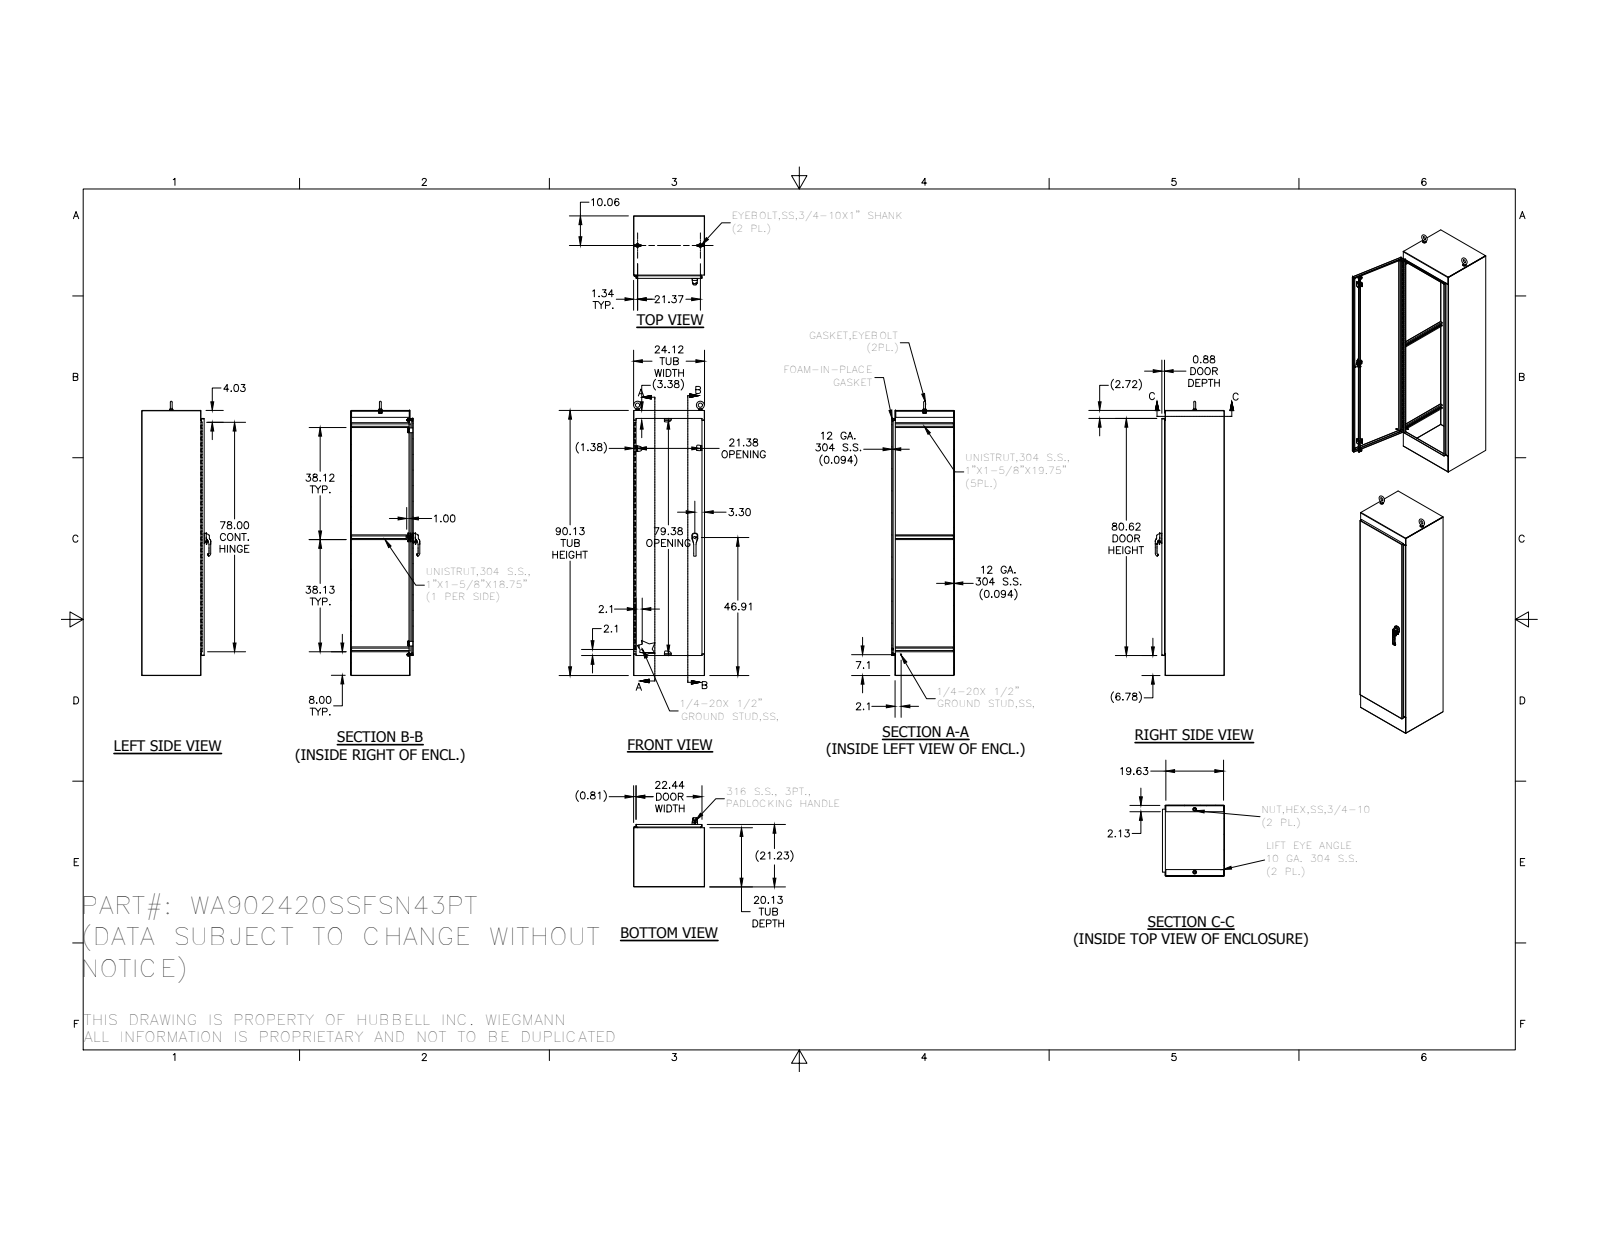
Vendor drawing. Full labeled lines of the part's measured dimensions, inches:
Part name (STEP PRODUCT): PLASTIC-ROLLER-CAM_AF0_ASM; 1091-903_AF0_2; DIN3771_16X2_5; 1091-76 (+8 more)
STEP written by: SolidWorks 2014 (AUTOMOTIVE_DESIGN)
Units: inches
Bodies: 66 solids, 3601 faces (1309 planar, 1352 cylindrical, 940 other)
Overall size (bounding box): 93.248 × 24.125 × 23.476
Volume: 1 033 in³ · Surface area: 21 416 in²
Round holes (diameter × count): ⌀0.262 ×8, ⌀0.375 ×8, ⌀0.187 ×4, ⌀0.213 ×3, ⌀0.25 ×3, ⌀0.28 ×3, ⌀0.241 ×2, ⌀0.252 ×2, ⌀0.315 ×2, ⌀0.4 ×2, ⌀0.402 ×2, ⌀0.413 ×2
Round bosses / shafts (diameter × count): ⌀1 ×3, ⌀0.236 ×3, ⌀1.25 ×2, ⌀1.12 ×2, ⌀0.75 ×2, ⌀0.563 ×2, ⌀0.533 ×2, ⌀0.531 ×2
Partial cylindrical surfaces — rounded edges, fillets, slot ends (radius × count): R0.02 ×172, R0.012 ×107, R0.125 ×26, R0.019 ×21, R0.05 ×19, R0.031 ×17, R0.079 ×14, R0.125 ×13
Main face-to-face distances: 0.094, 21.133, 24.031, 21.039, 23.937, 24.125, 21.227, 90.031, 20.031, 1.102
Hole centre spacings: 8.667, 26, 0.38, 0.76, 2.763, 17.333, 34.667, 0.38
